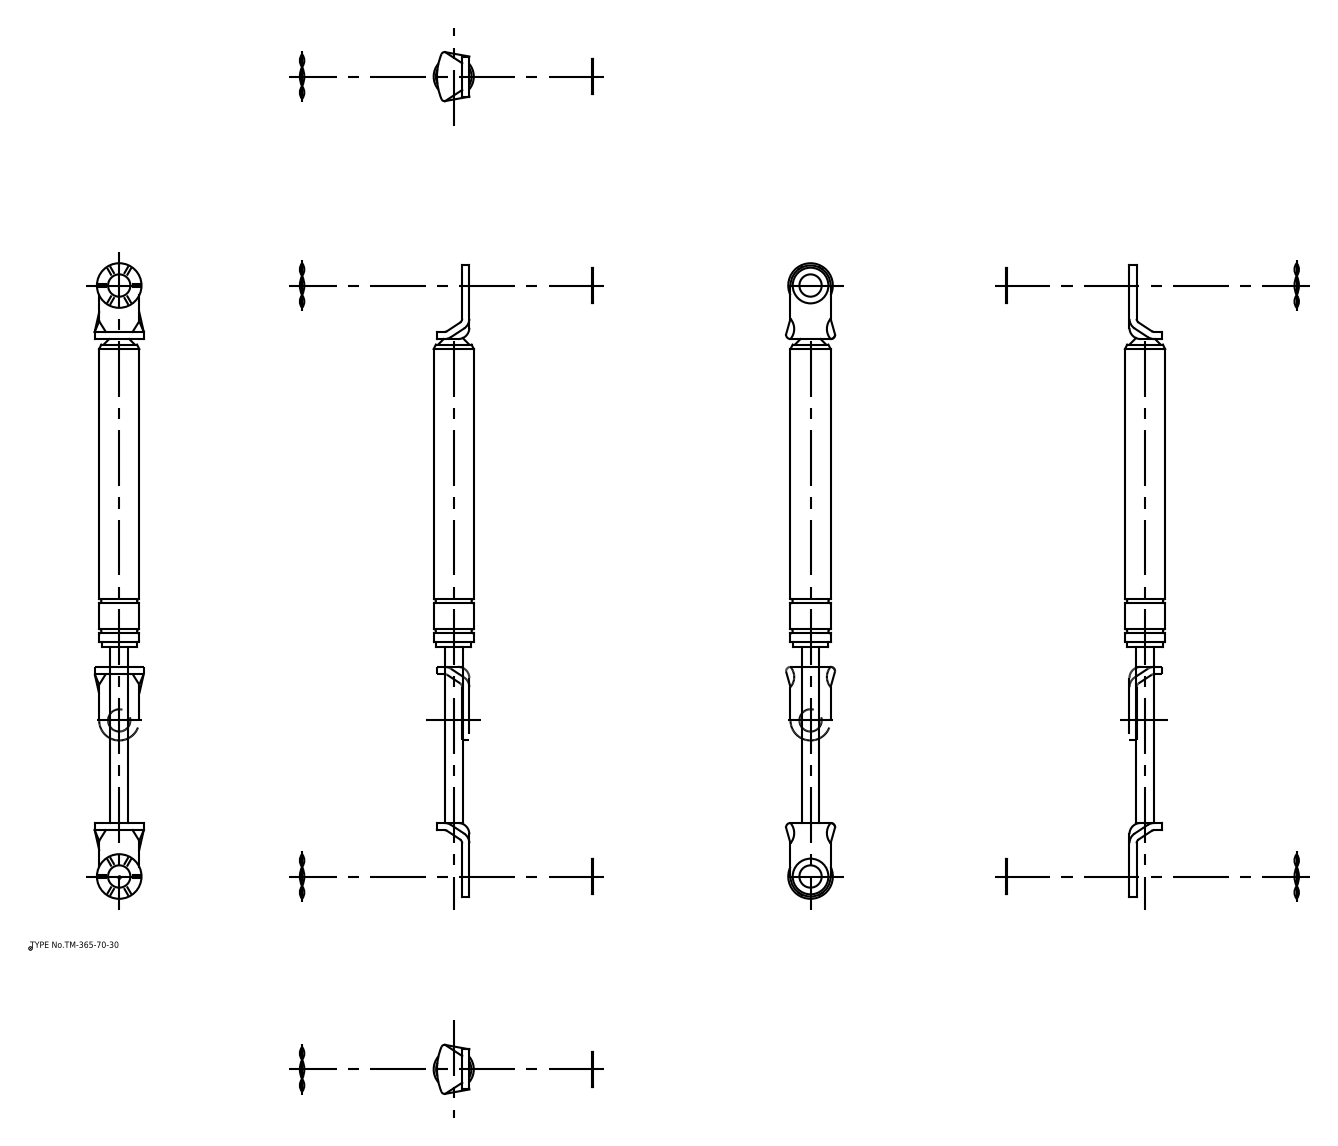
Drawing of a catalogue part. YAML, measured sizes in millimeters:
part_name: "ウェーブワッシャー; ワッシャー; 本体; 本体_div"
step_written_by: "spGate 16.7.1 (AUTOMOTIVE_DESIGN)"
units: millimeters
bodies: {solids: 6, faces: 94, planar: 42, cylindrical: 44, other: 8}
overall_size: [285, 22, 18.5]
volume: 44063
surface_area: 15802
round_holes:
  - {diameter: 10, count: 2}
round_bosses_or_shafts:
  - {diameter: 16, count: 3}
  - {diameter: 20, count: 2}
  - {diameter: 18.5, count: 1}
  - {diameter: 18, count: 1}
  - {diameter: 8, count: 1}
partial_cylinders:
  - {radius: 4.4, count: 2}
  - {radius: 5, count: 2}
  - {radius: 9, count: 2}
  - {radius: 26.32, count: 1}
face_to_face_distances: [3.2, 2, 5.2, 220.2, 3.7, 5.7, 0.5, 141.2, 82.2, 223.4]
hole_center_spacings: [265]
